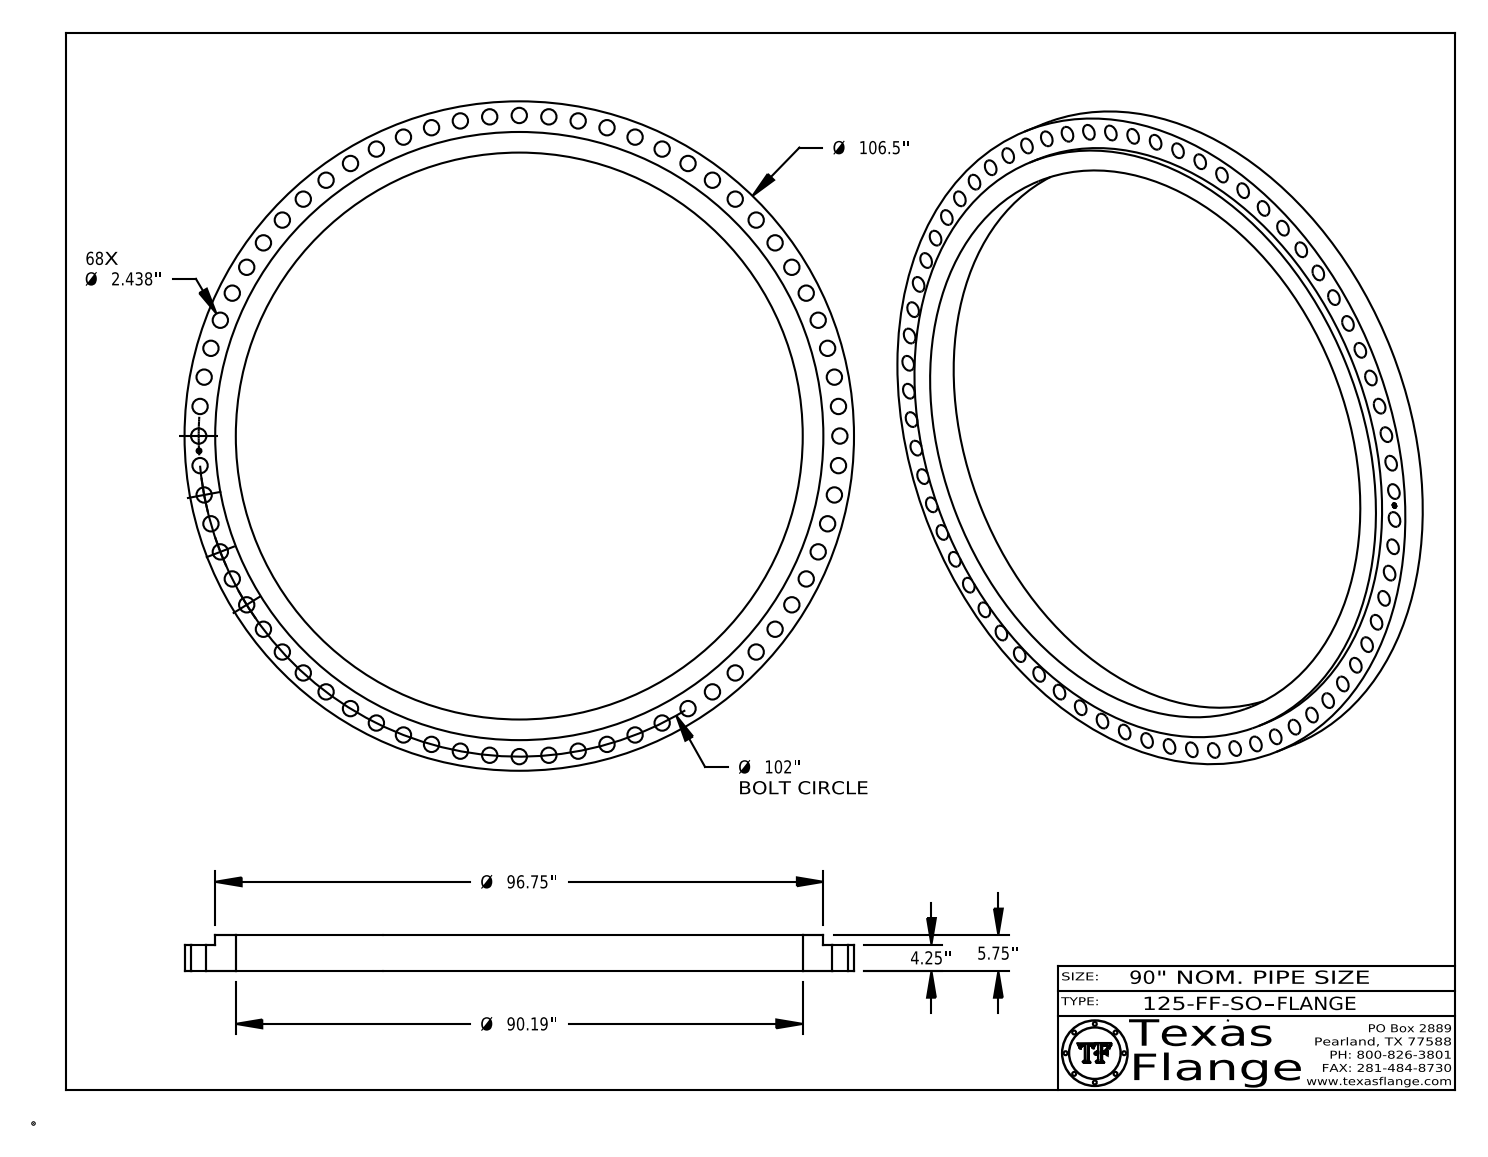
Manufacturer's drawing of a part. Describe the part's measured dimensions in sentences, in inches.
The part is named "125-FF-SO-B16.1". Its 3-D file was written by "CATIA V5 STEP AP214 (AUTOMOTIVE_DESIGN)". It is 1 solid with 530 faces: 368 planar, 162 cylindrical and 0 other. Overall it measures 106.5 by 106.5 by 5.75 inches. Its volume is 10 804 cubic inches and its surface area 10 125 square inches. Round holes: 68 of diameter 2.438, 1 of diameter 0.75, 1 of diameter 90.19. Round bosses or shafts: 8 of diameter 0.045, 1 of diameter 106.5, 1 of diameter 96.75, 1 of diameter 0.591. The main face-to-face distances are 4.25, 5.75, 1.5, 4.235, 0.015, 1.515, 0.224, 0.219, 0.041, 0.145. The hole center spacings are 51, 9.411, 18.743, 4.711, 23.353, 14.092, 32.415, 41.2.
